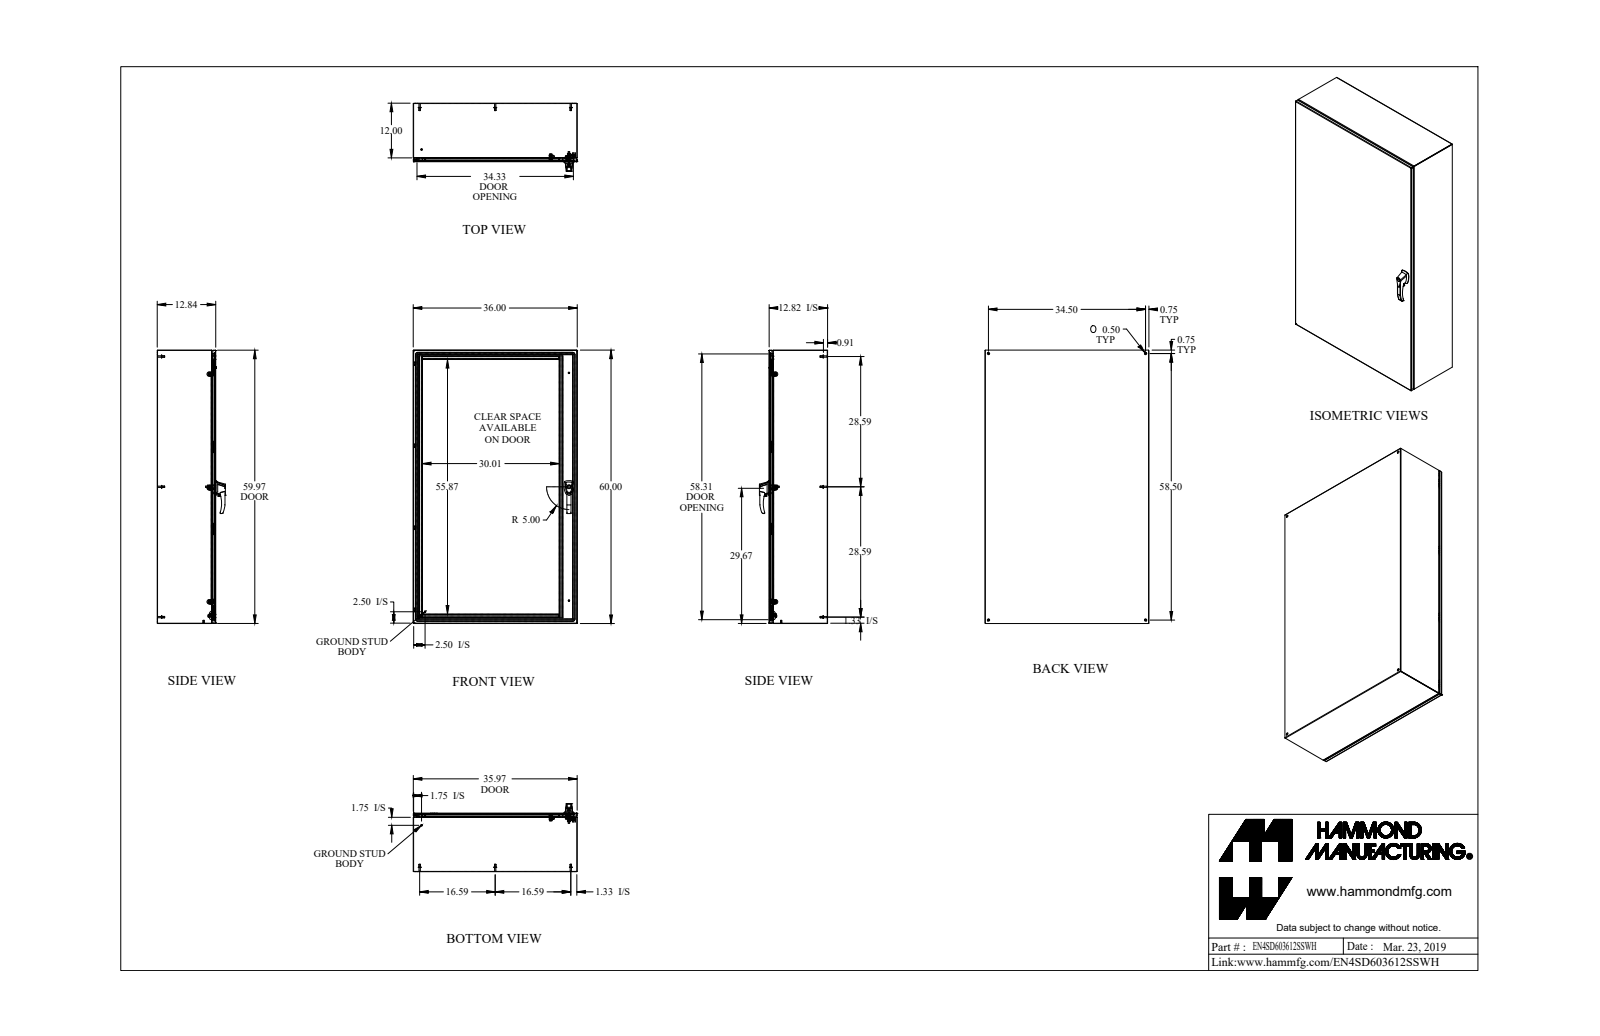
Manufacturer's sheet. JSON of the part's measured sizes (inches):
{"part_name": "EN4SD603612SSWH", "step_written_by": "SolidWorks 2018 (AUTOMOTIVE_DESIGN)", "units": "inches", "bodies": {"solids": 68, "faces": 1783, "planar": 779, "cylindrical": 669, "other": 335}, "overall_size": [60, 36, 14.958], "volume_in3": 561, "surface_area_in2": 15609, "round_holes": [[0.176, 6], [0.5, 4], [0.196, 3], [0.25, 3], [0.265, 3], [0.313, 3], [0.413, 3], [0.256, 2], [0.375, 2], [0.394, 2], [0.172, 1], [0.233, 1]], "round_bosses_or_shafts": [[0.313, 10], [0.625, 9], [0.275, 8], [0.25, 7], [0.375, 6], [0.156, 6], [1, 3], [0.51, 3]], "partial_cylinders_radius": [[0.043, 24], [0.036, 18], [0.108, 18], [0.062, 17], [0.094, 10], [0.016, 9], [0.125, 9], [0.006, 8]], "face_to_face_distances": [0.072, 12.771, 12.699, 12.843, 35.928, 59.928, 35.856, 36, 59.856, 60], "hole_center_spacings": [0.786, 4.395, 24.984, 24.985, 24.985, 25, 29.269, 33.71]}
